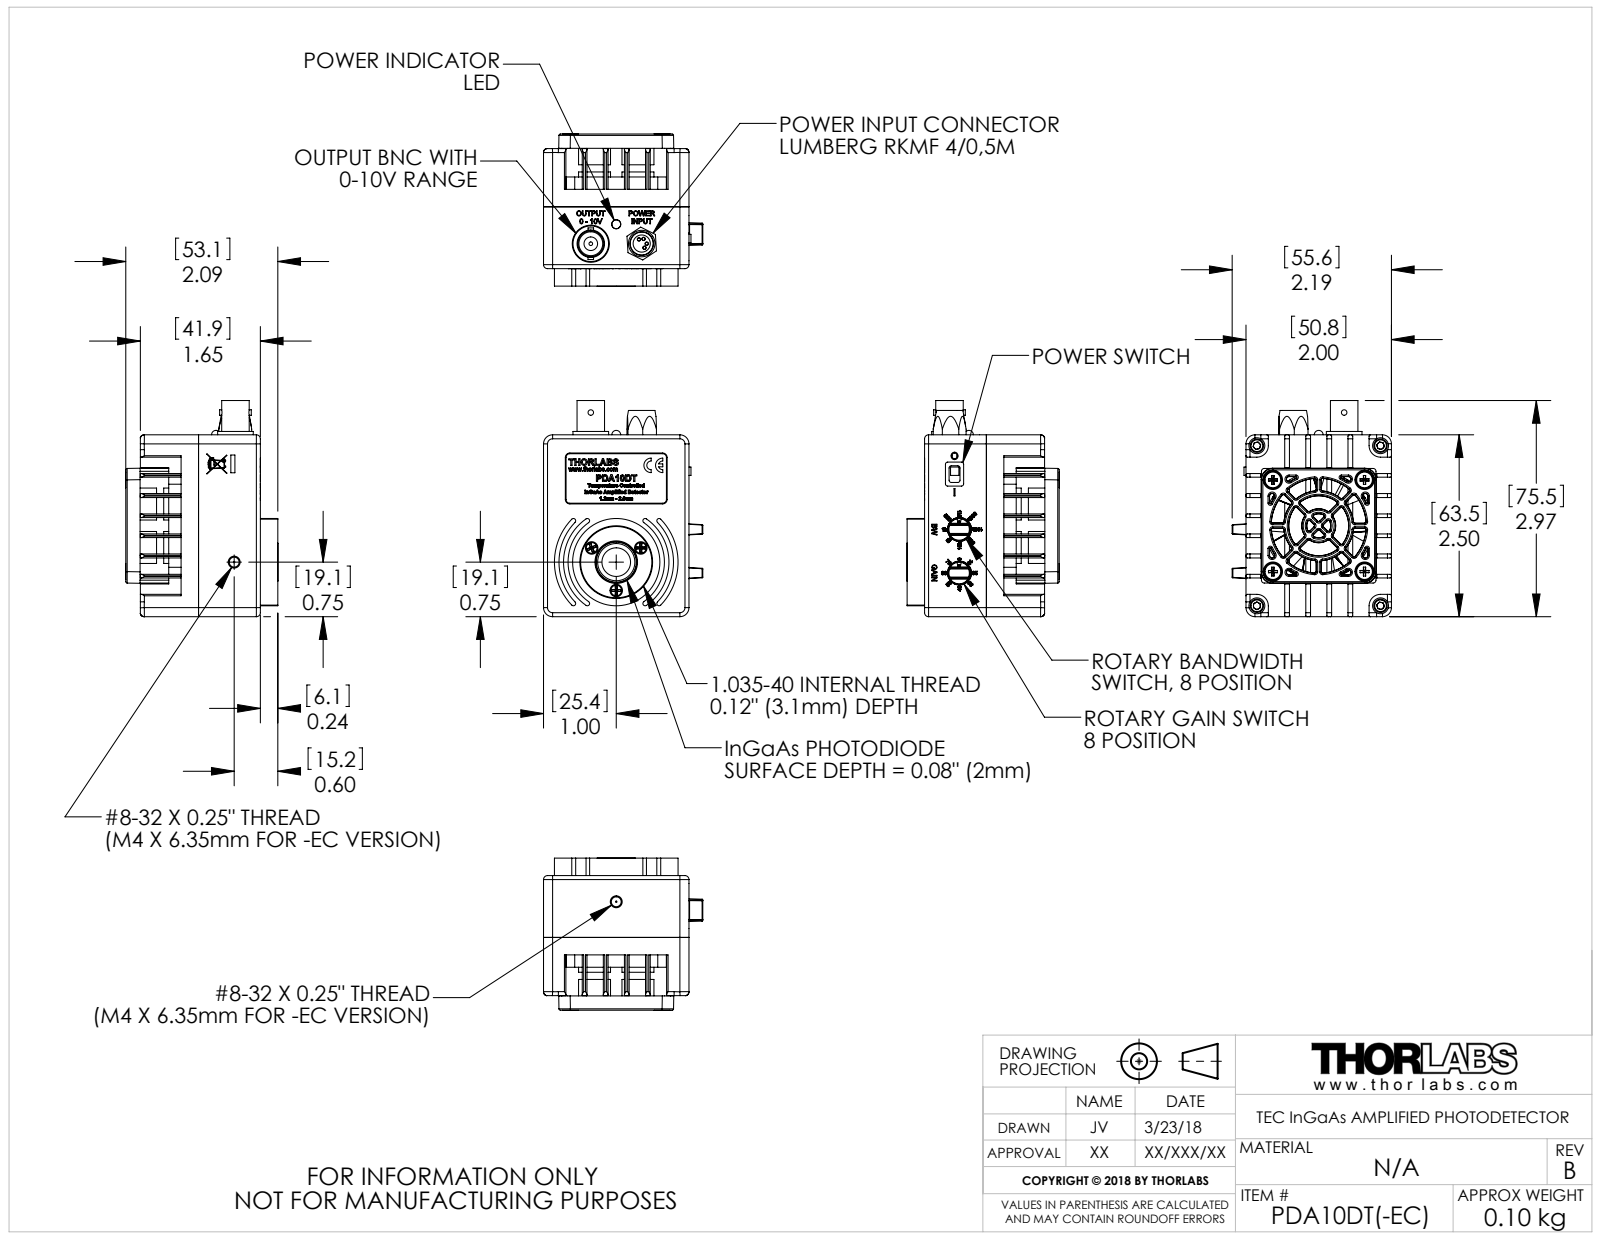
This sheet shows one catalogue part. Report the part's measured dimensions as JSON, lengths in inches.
{"part_name": "13129-E0W", "step_written_by": "SolidWorks 2007 (AUTOMOTIVE_DESIGN)", "units": "inches", "bodies": {"solids": 33, "faces": 4435, "planar": 2218, "cylindrical": 754, "other": 1463}, "overall_size": [2.971, 2.19, 2.094], "volume_in3": 3.953, "surface_area_in2": 95.31, "round_holes": [[0.086, 11], [0.07, 8], [0.096, 7], [0.059, 6], [0.063, 6], [0.032, 4], [0.039, 4], [0.089, 4], [0.098, 4], [0.112, 4], [0.129, 4], [0.169, 4]], "round_bosses_or_shafts": [[0.016, 8], [0.018, 6], [0.217, 4], [0.125, 4], [0.118, 4], [0.147, 3], [1.491, 1], [1.2, 1]], "partial_cylinders_radius": [[0.02, 48], [0.02, 32], [0.1, 22], [0.031, 18], [0.01, 11], [0.055, 8], [0.125, 8], [0.01, 4]], "face_to_face_distances": [0.24, 0.533, 0.05, 1.09, 0.8, 0.065, 0.483, 1.04, 0.85, 0.58], "hole_center_spacings": [0.224, 0.069, 0.317, 0.449, 0.463, 0.519, 0.6, 1.214]}
